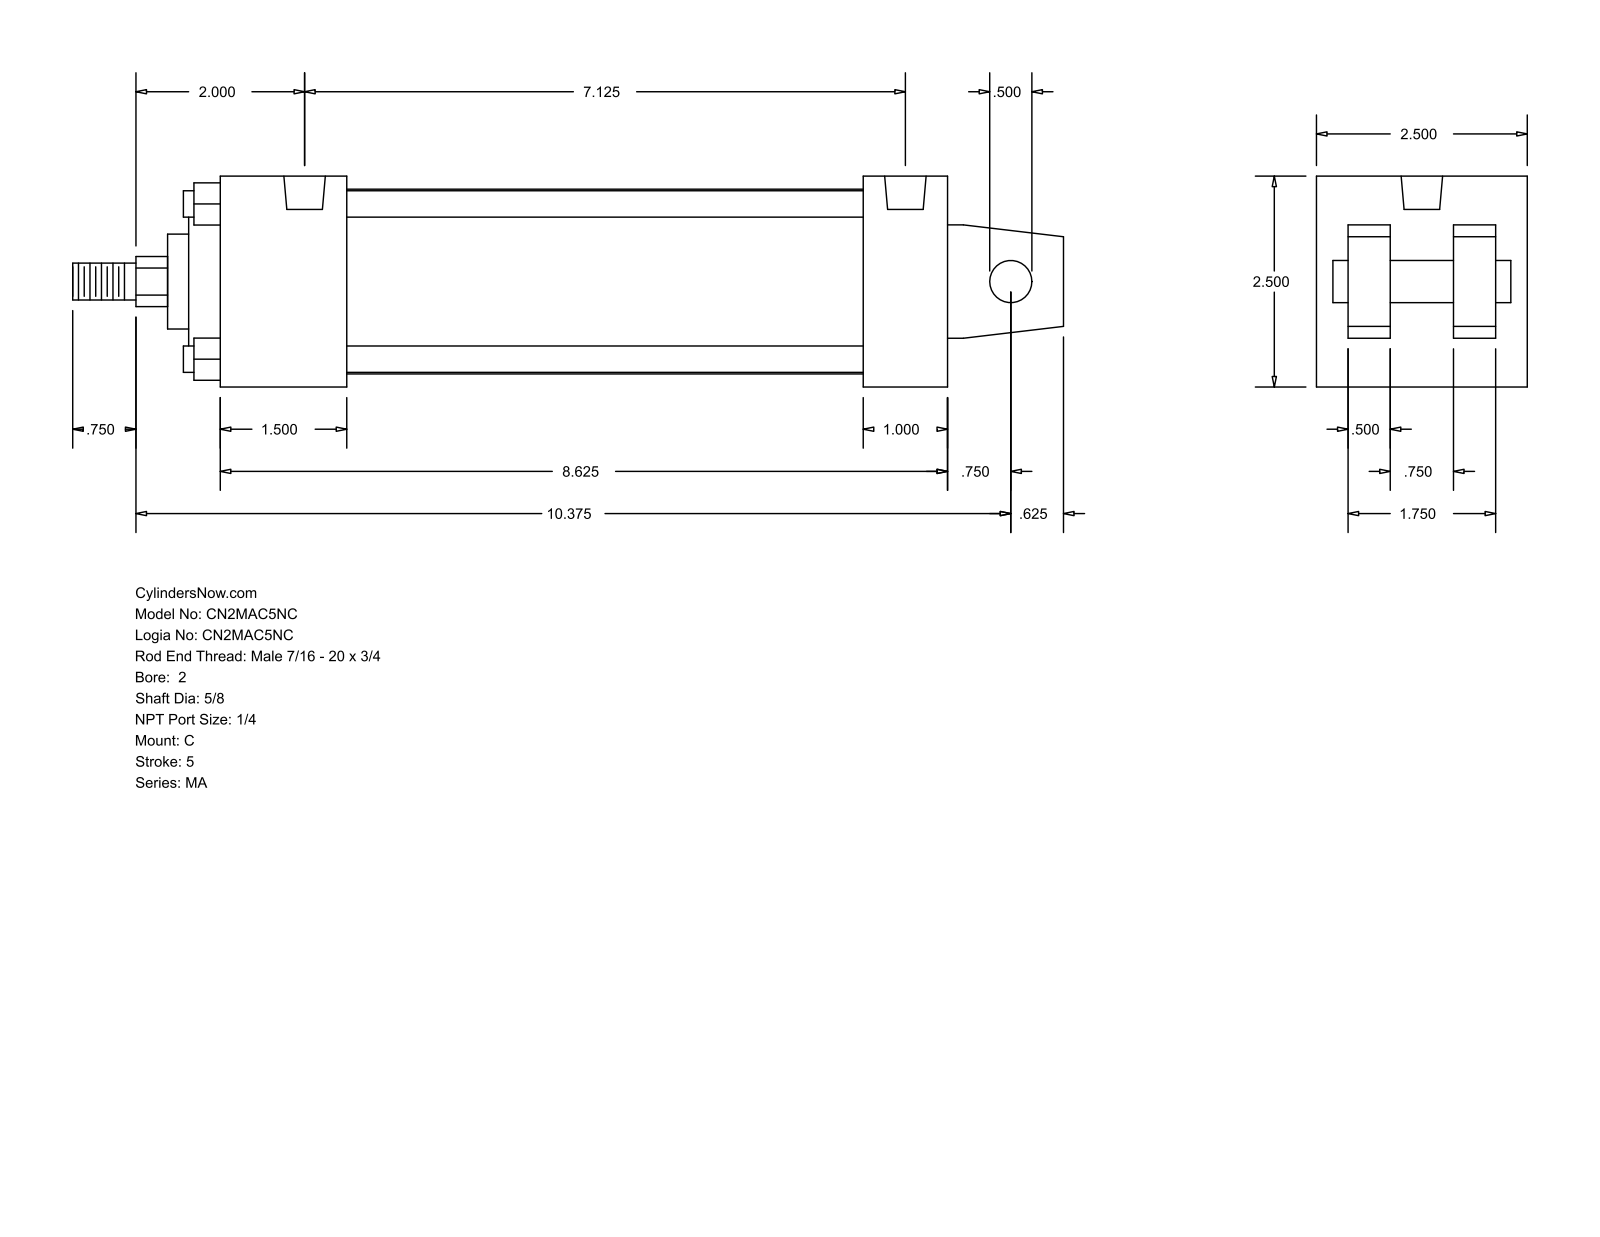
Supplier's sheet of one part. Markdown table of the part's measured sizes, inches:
| quantity | value |
| --- | --- |
| part name | MA_C__0200_0.625 |
| STEP written by | GSSL Pune (CONFIG_CONTROL_DESIGN) |
| units | inches |
| bodies | 0 solids, 105 faces (77 planar, 28 cylindrical, 0 other) |
| overall size | 11.75 × 2.5 × 2.5 |
| round holes (diameter × count) | 0.313 × 4, 0.492 × 2 |
| round bosses / shafts (diameter × count) | 0.313 × 4, 2.19 × 1, 2 × 1, 1.125 × 1, 0.625 × 1, 0.5 × 1, 0.437 × 1 |
| partial cylindrical surfaces (radius × count) | 0.297 × 1 |
| main face-to-face distances | 2.5, 0.375, 0.5, 0.875, 1.625, 2.125, 1.25, 1, 1.5, 8.625 |
| hole center spacings | 7.125 |
